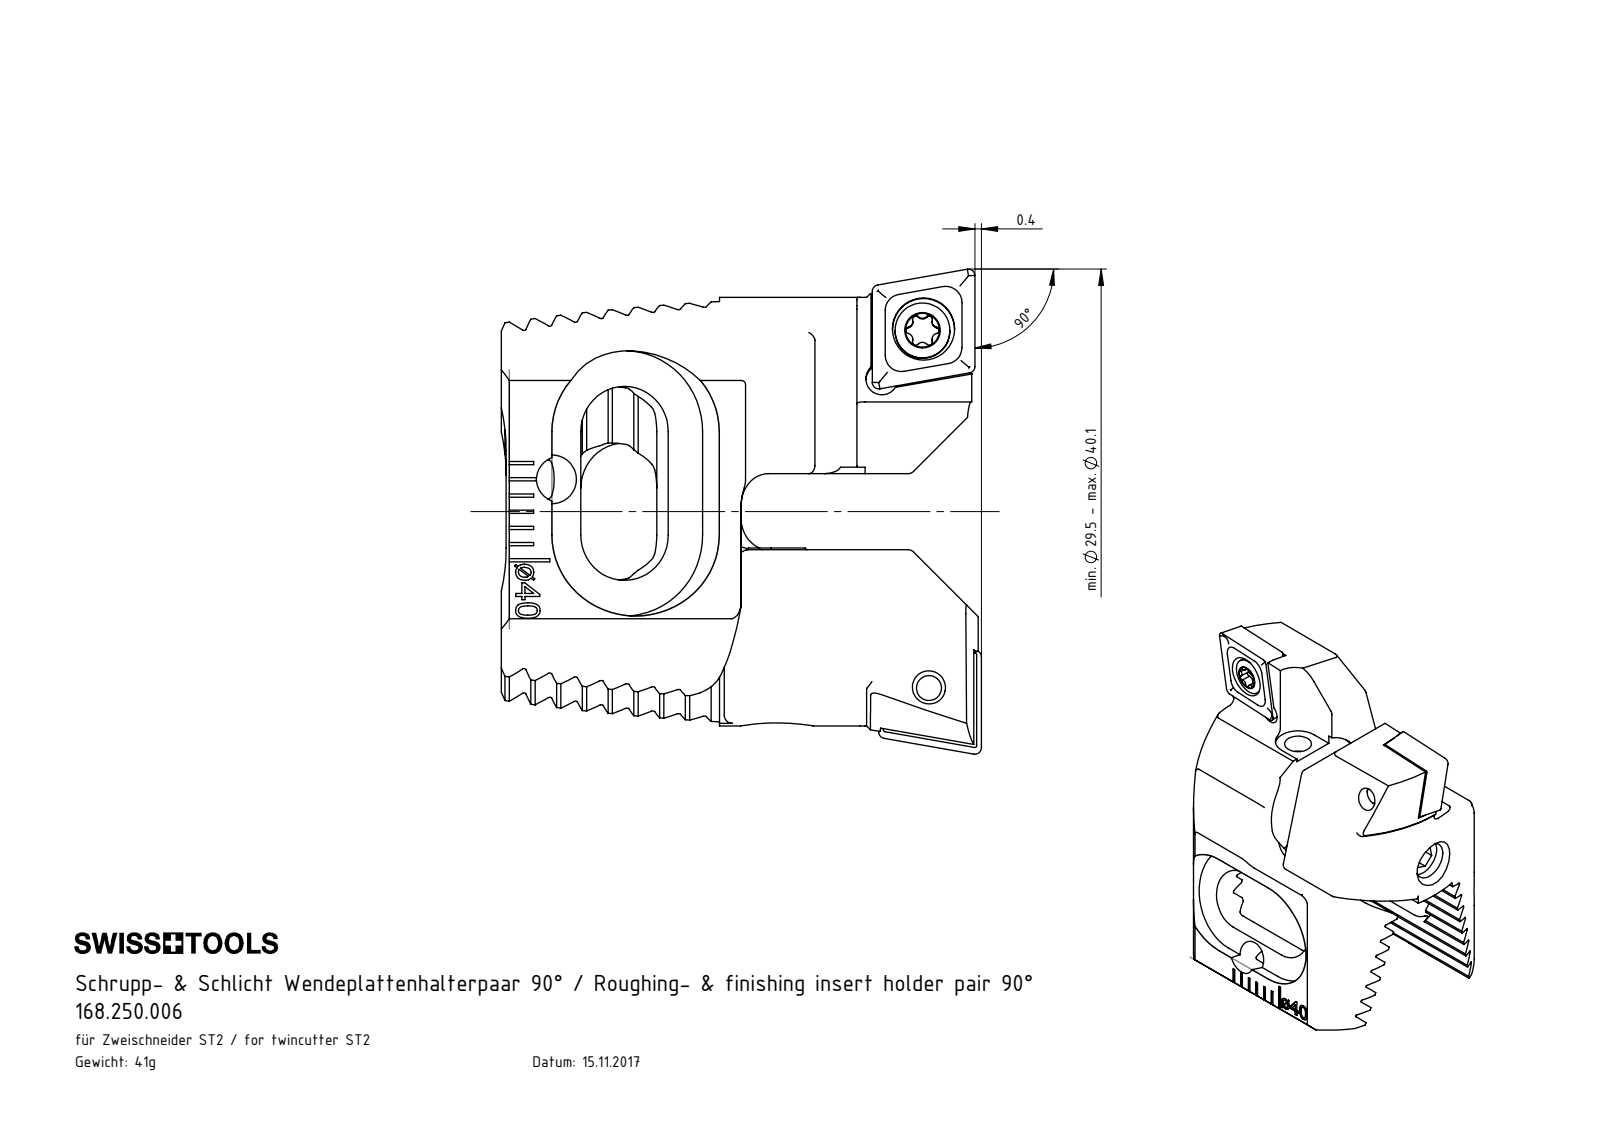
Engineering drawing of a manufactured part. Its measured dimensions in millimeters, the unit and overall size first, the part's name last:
Units: millimetres
Overall size (bounding box): 30 × 29.7 × 20.29
Round holes (diameter × count): ⌀2 ×2, ⌀2.05 ×2, ⌀2.8 ×2, ⌀3.85 ×2, ⌀1.6 ×1, ⌀2.5 ×1, ⌀3 ×1, ⌀3.5 ×1
Round bosses / shafts (diameter × count): ⌀3.4 ×2, ⌀2.5 ×2, ⌀4 ×1, ⌀3 ×1, ⌀2 ×1
Partial cylindrical surfaces — rounded edges, fillets, slot ends (radius × count): R0.5 ×18, R0.12 ×16, R0.21 ×12, R0.36 ×10, R2 ×4, R2.8 ×4, R5 ×4, R12 ×4
Main face-to-face distances: 1.43, 2.86, 4.29, 5.72, 7.15, 3.9, 8.58, 1.01, 0.4, 5.1
Hole centre spacings: 3.9, 4, 7, 16.42, 19.51, 19.6, 19.61, 19.7
Volume: 5 153 mm³ · Surface area: 4 688 mm²
Bodies: 8 solids, 653 faces (328 planar, 143 cylindrical, 182 other)
Part name (STEP PRODUCT): ZC2-xxx.001.016_A; WCA-ER2.001.006_A; ISO 4028 - M3 x 5_M3x6; Z25-ER3.001.010_A (+3 more)
STEP written by: SolidWorks 2017 (CONFIG_CONTROL_DESIGN)
